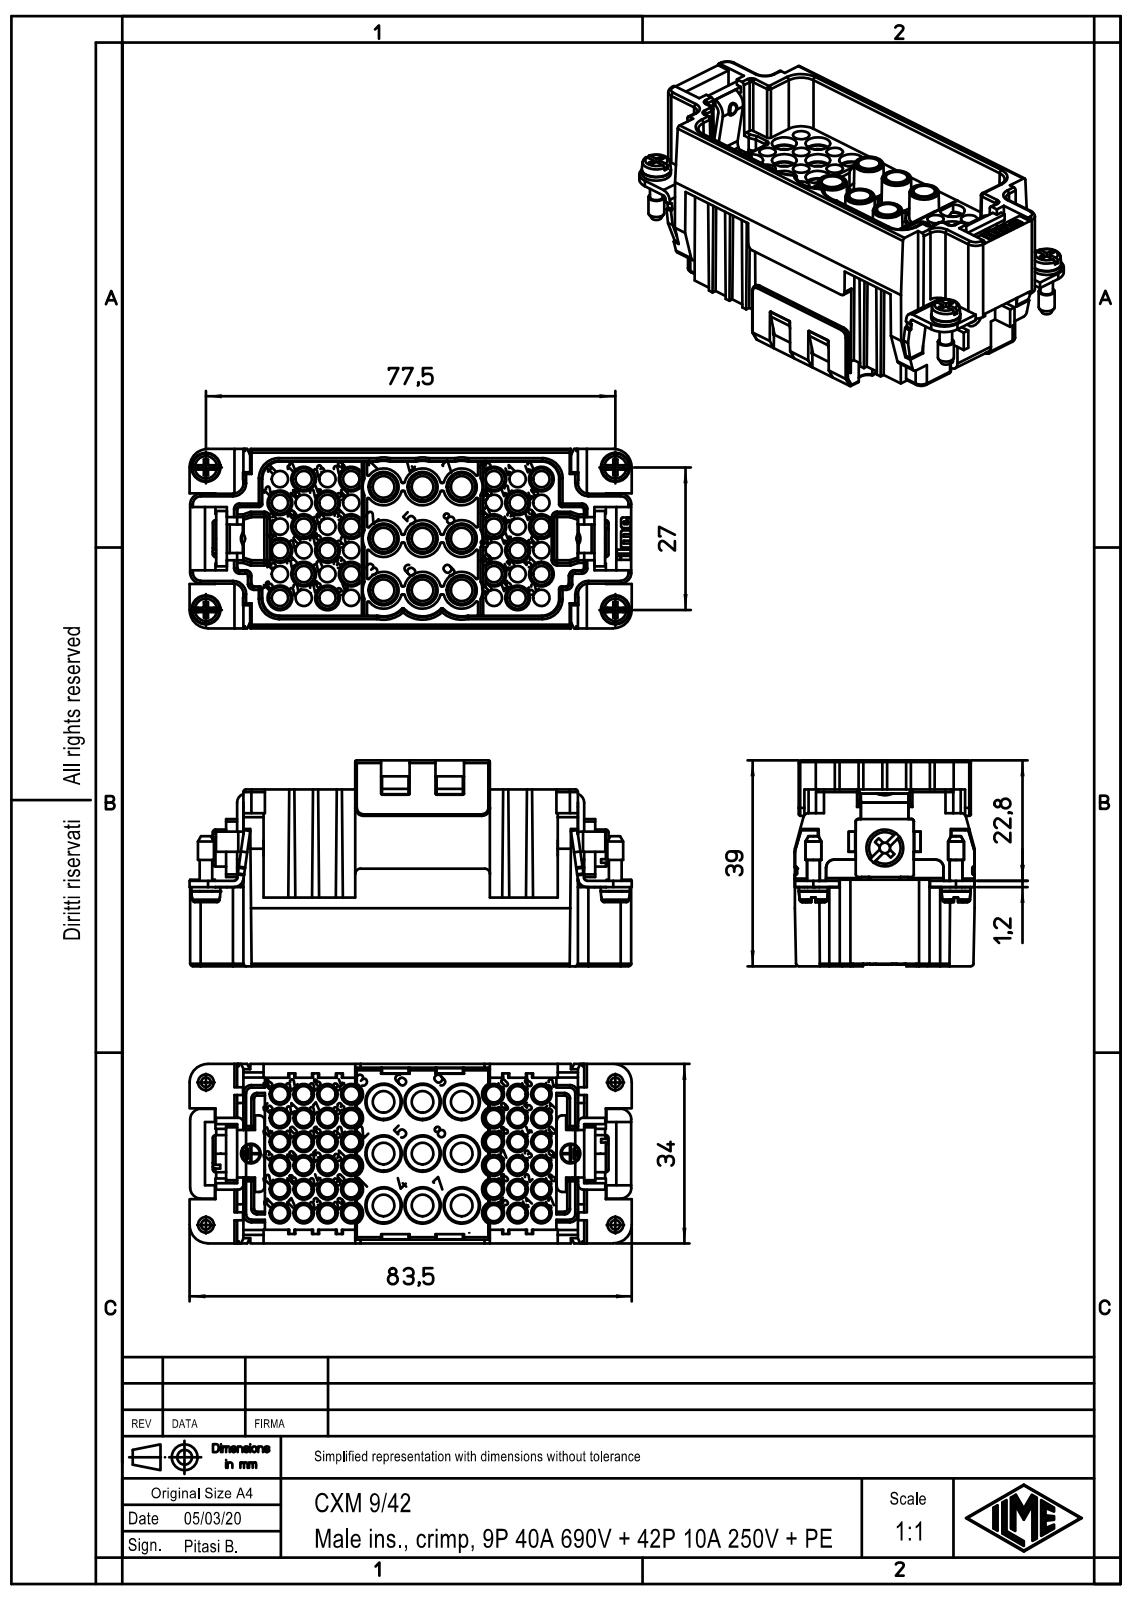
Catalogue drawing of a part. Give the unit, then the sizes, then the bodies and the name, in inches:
Units: inches
Overall size (bounding box): 3.295 × 1.535 × 1.339
Round holes (diameter × count): ⌀0.102 ×42, ⌀0.128 ×42, ⌀0.154 ×42, ⌀0.185 ×13, ⌀0.112 ×9, ⌀0.161 ×9, ⌀0.256 ×9, ⌀0.11 ×4, ⌀0.079 ×1, ⌀0.13 ×1
Round bosses / shafts (diameter × count): ⌀0.236 ×9, ⌀0.276 ×4, ⌀0.217 ×4, ⌀0.118 ×4, ⌀0.094 ×4, ⌀0.224 ×1, ⌀0.157 ×1
Partial cylindrical surfaces — rounded edges, fillets, slot ends (radius × count): R0.02 ×87, R0.012 ×53, R0.039 ×18, R0.008 ×14, R0.126 ×11, R0.079 ×10, R0.138 ×10, R0.173 ×9
Main face-to-face distances: 0.031, 0.079, 0.217, 1.165, 0.047, 0.159, 2.333, 0.886, 0.059, 1.197
Hole centre spacings: 0.177, 0.396, 0.25, 0.354, 0.56, 0.531, 0.483, 0.501
Volume: 2.249 in³ · Surface area: 62.62 in²
Bodies: 1 solid, 2837 faces (1197 planar, 769 cylindrical, 871 other)
Part name (STEP PRODUCT): CXM 9-42
STEP written by: Creo Elements/Direct Modeling 20.1B 02-Apr-2019 (C) Parametric Technology GmbH (AUTOMOTIVE_DESIGN)
